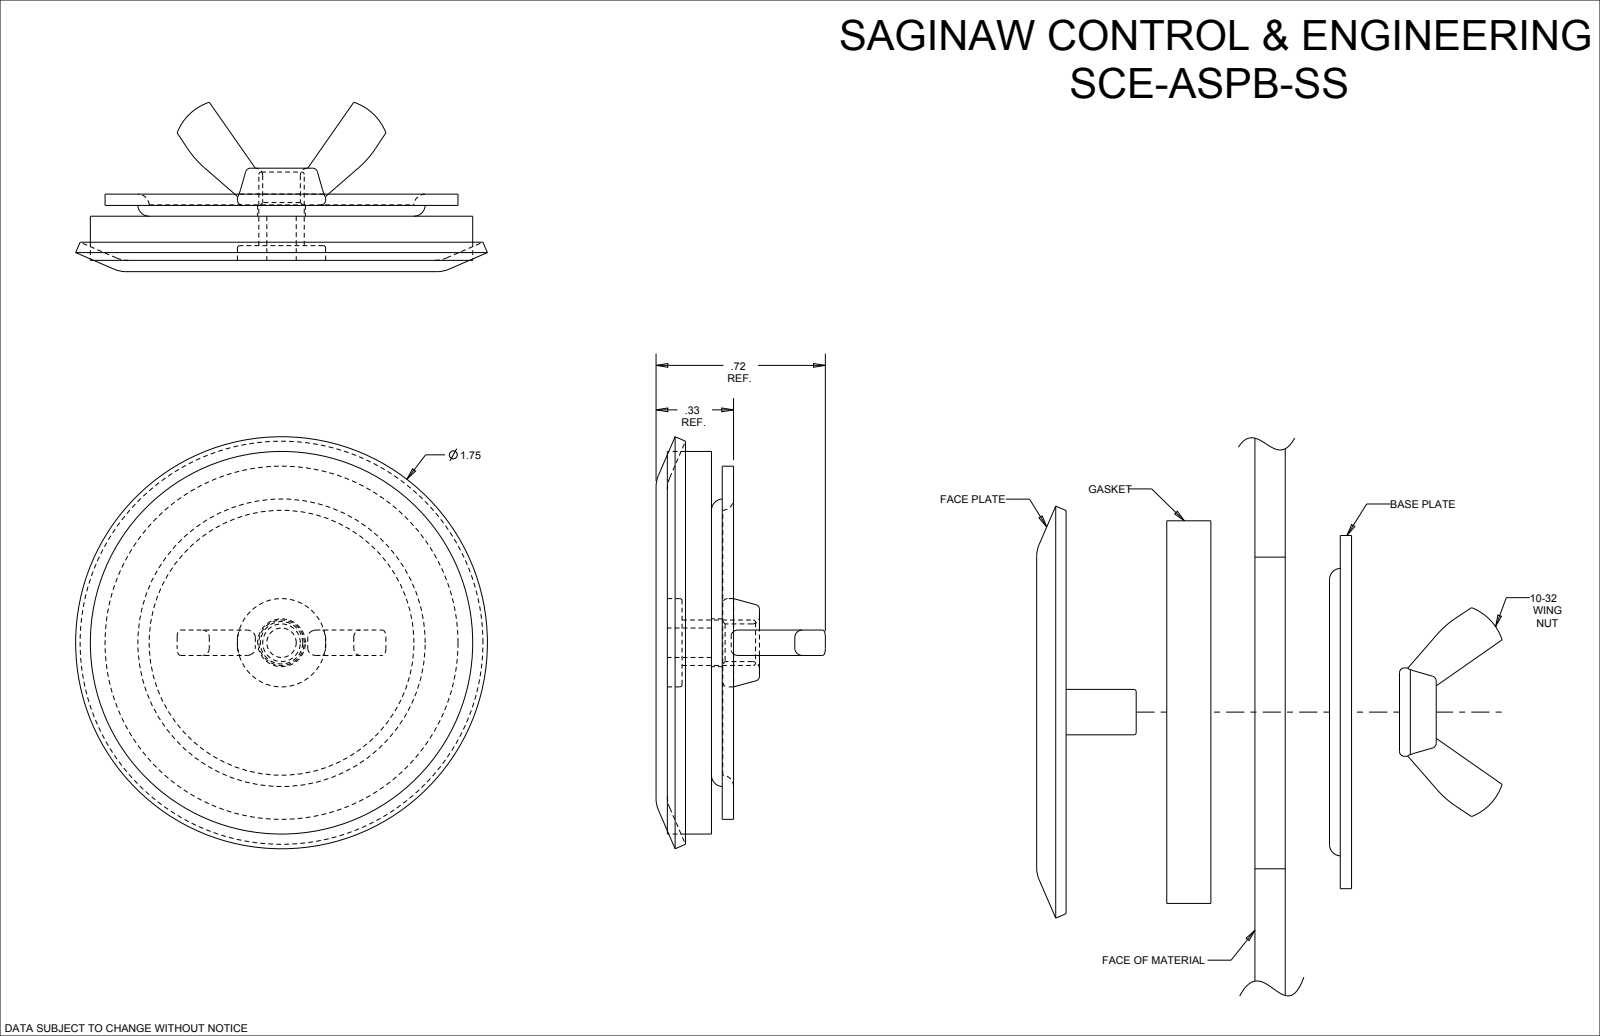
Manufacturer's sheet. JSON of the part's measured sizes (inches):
{"part_name": "SCE-ASPB-SS", "step_written_by": "SolidWorks 2019 (CONFIG_CONTROL_DESIGN)", "units": "inches", "bodies": {"solids": 5, "faces": 71, "planar": 27, "cylindrical": 24, "other": 20}, "overall_size": [1.75, 1.75, 0.719], "volume_in3": 0.632, "surface_area_in2": 15.42, "round_holes": [[0.125, 1], [0.16, 1], [0.203, 1]], "round_bosses_or_shafts": [[1.625, 1], [1.5, 1], [0.375, 1], [0.193, 1]], "partial_cylinders_radius": [[0.03, 12], [0.22, 2], [0.4, 2]], "face_to_face_distances": [0.187, 0.048, 0.235, 0.046, 0.281, 0.283, 0.094, 0.33, 0.233, 0.108]}
